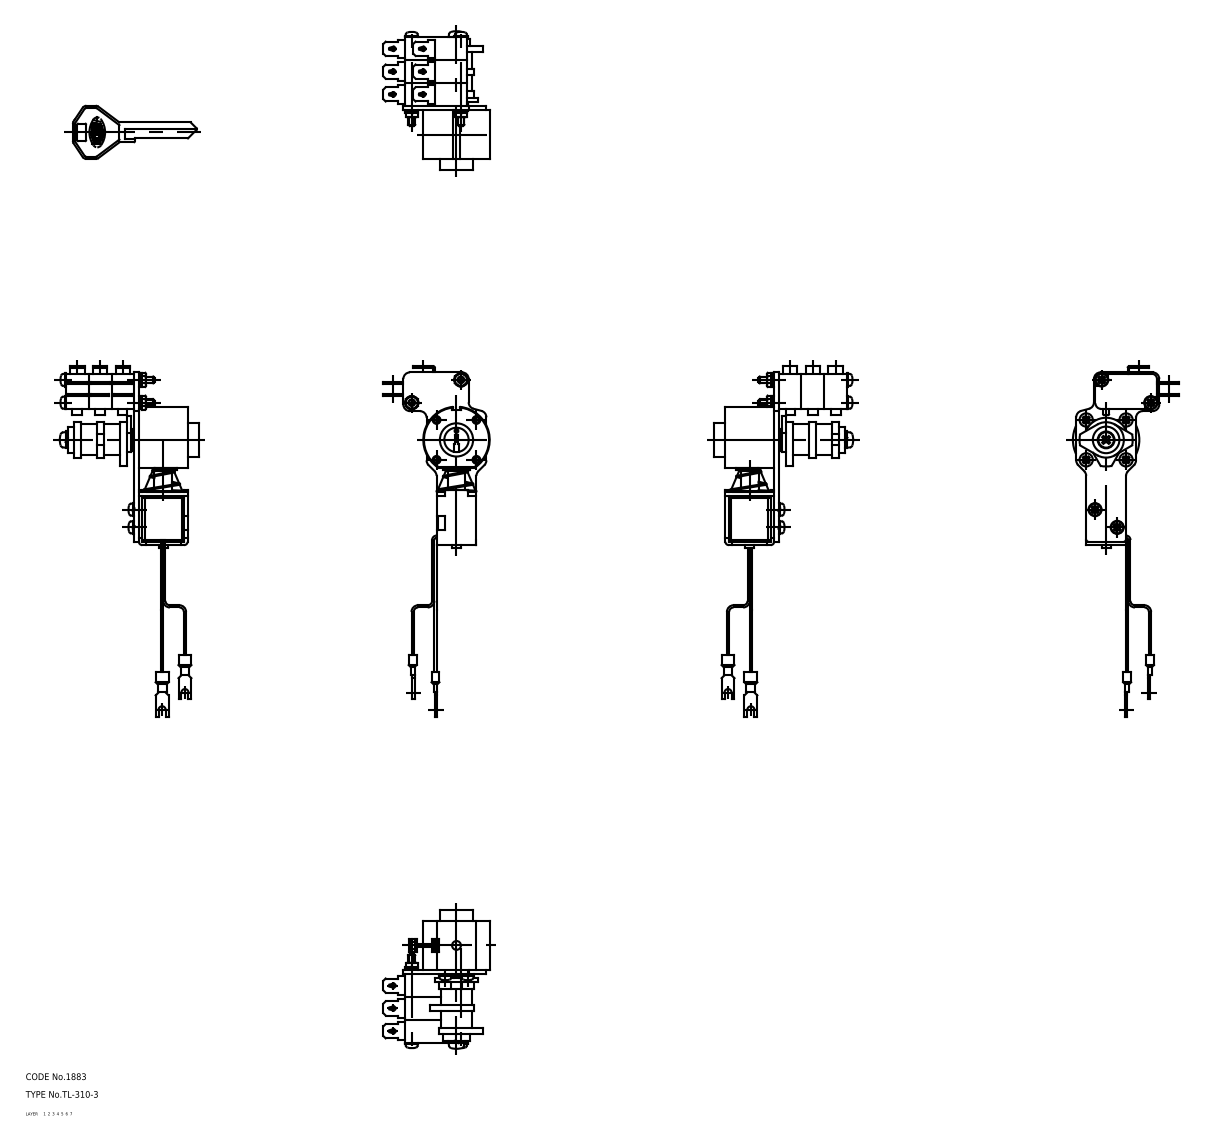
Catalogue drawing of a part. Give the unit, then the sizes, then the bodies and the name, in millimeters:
Units: millimetres
Overall size (bounding box): 153.78 × 152.14 × 48
Volume: 47 248 mm³ · Surface area: 29 557 mm²
Bodies: 25 solids, 857 faces (0 planar, 0 cylindrical, 857 other)
Part name (STEP PRODUCT): spring; screw_2; screw_3; screw_4 (+8 more)
STEP written by: CADfix (AUTOMOTIVE_DESIGN)
